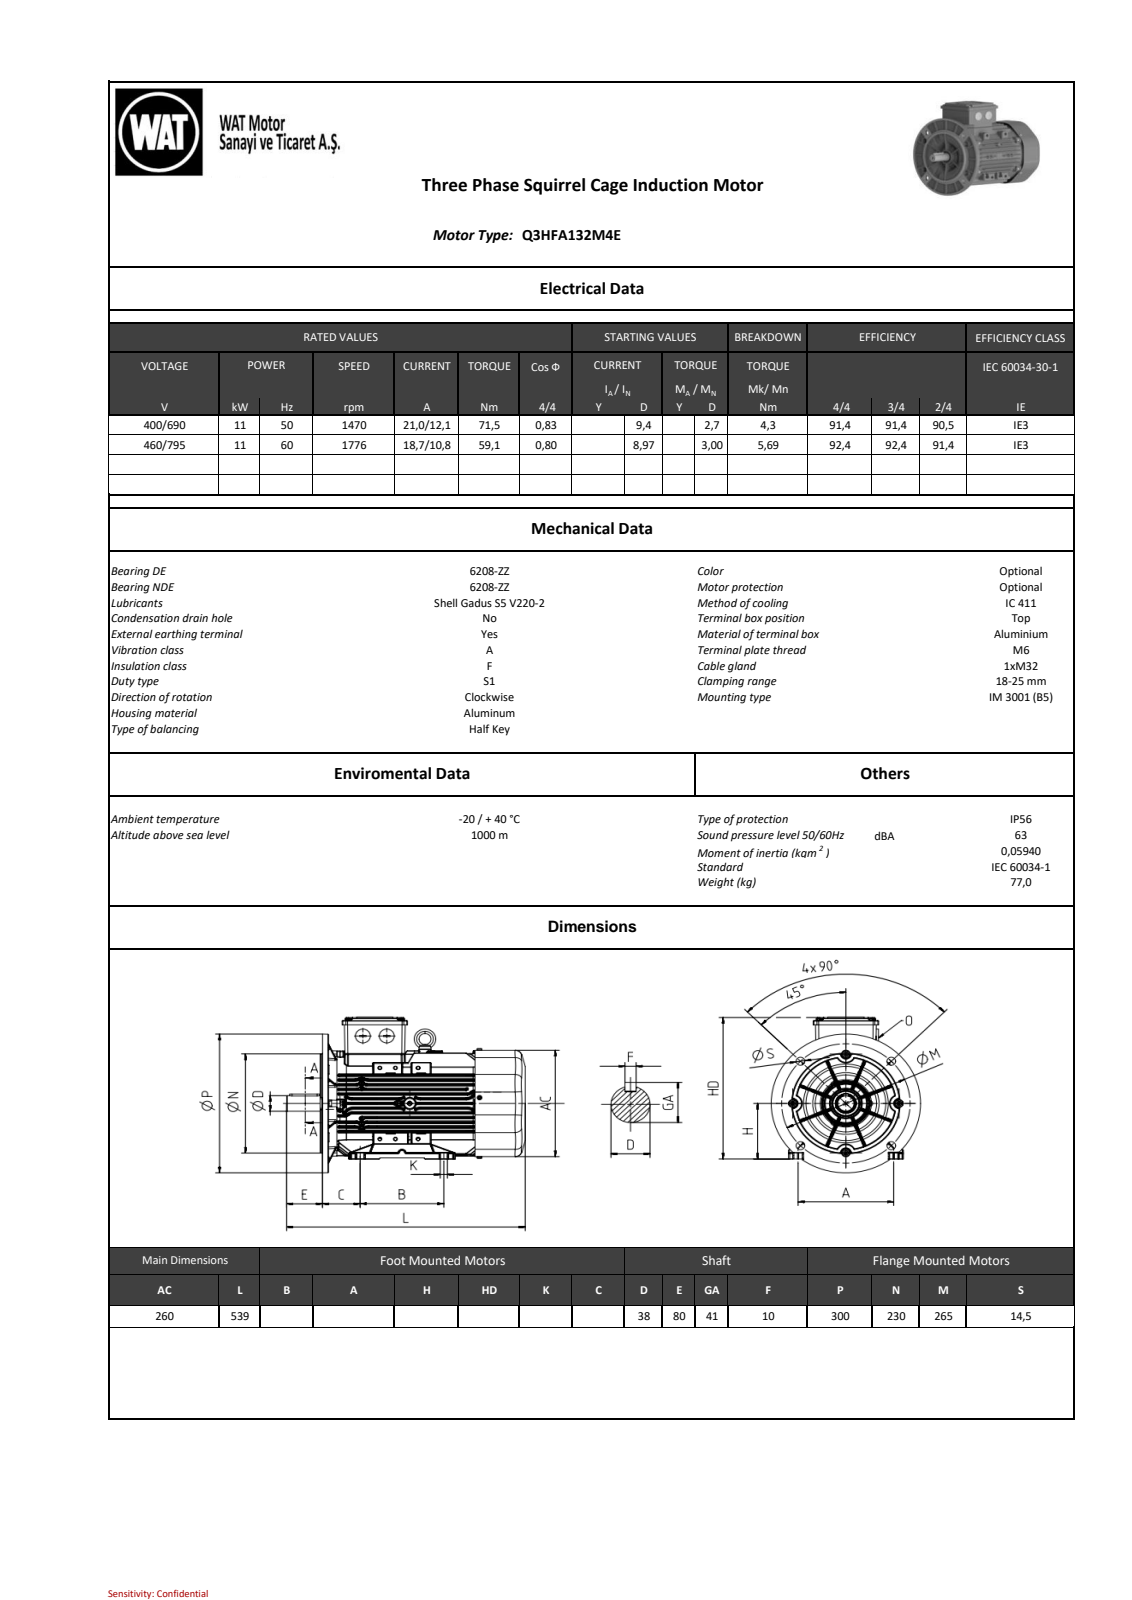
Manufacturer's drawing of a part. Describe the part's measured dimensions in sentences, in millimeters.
The part is named "QH series_ 132_B5 _DEEP COVER__stp_objects". Its 3-D file was written by "SIEMENS PLM Software NX2206.8101 (AP203_CONFIGURATION_CONTROLLED_3D_DESIGN_OF_MECHANICAL_PARTS_AND_ASSEMBLIES_MIM_LF)". It is 0 solids with 7375 faces: 1836 planar, 3232 cylindrical and 2307 other. Overall it measures 538.95 by 340.18 by 299.95 millimeters. Round holes: 1 of diameter 8, 1 of diameter 8.47, 1 of diameter 8.48, 1 of diameter 8.48, 1 of diameter 12, 1 of diameter 13, 1 of diameter 34.5, 1 of diameter 62, 1 of diameter 82, 1 of diameter 180, 1 of diameter 225. Round bosses or shafts: 8 of diameter 8, 4 of diameter 13, 3 of diameter 38, 1 of diameter 230.5, 1 of diameter 230, 1 of diameter 86.77, 1 of diameter 40, 1 of diameter 37.4. Partial cylindrical surfaces (rounded edges, fillets, slot ends): 1000 of radius 0.8, 861 of radius 1, 93 of radius 0.5, 64 of radius 3, 60 of radius 2, 57 of radius 1.5, 18 of radius 5, 16 of radius 60. The main face-to-face distances are 10.42, 1.5, 10.56, 10.28, 20.84, 125.58, 115.18, 104.9, 9.5, 4.5. The hole center spacings are 0.67, 89.32, 103.84, 114.16, 178.91.
